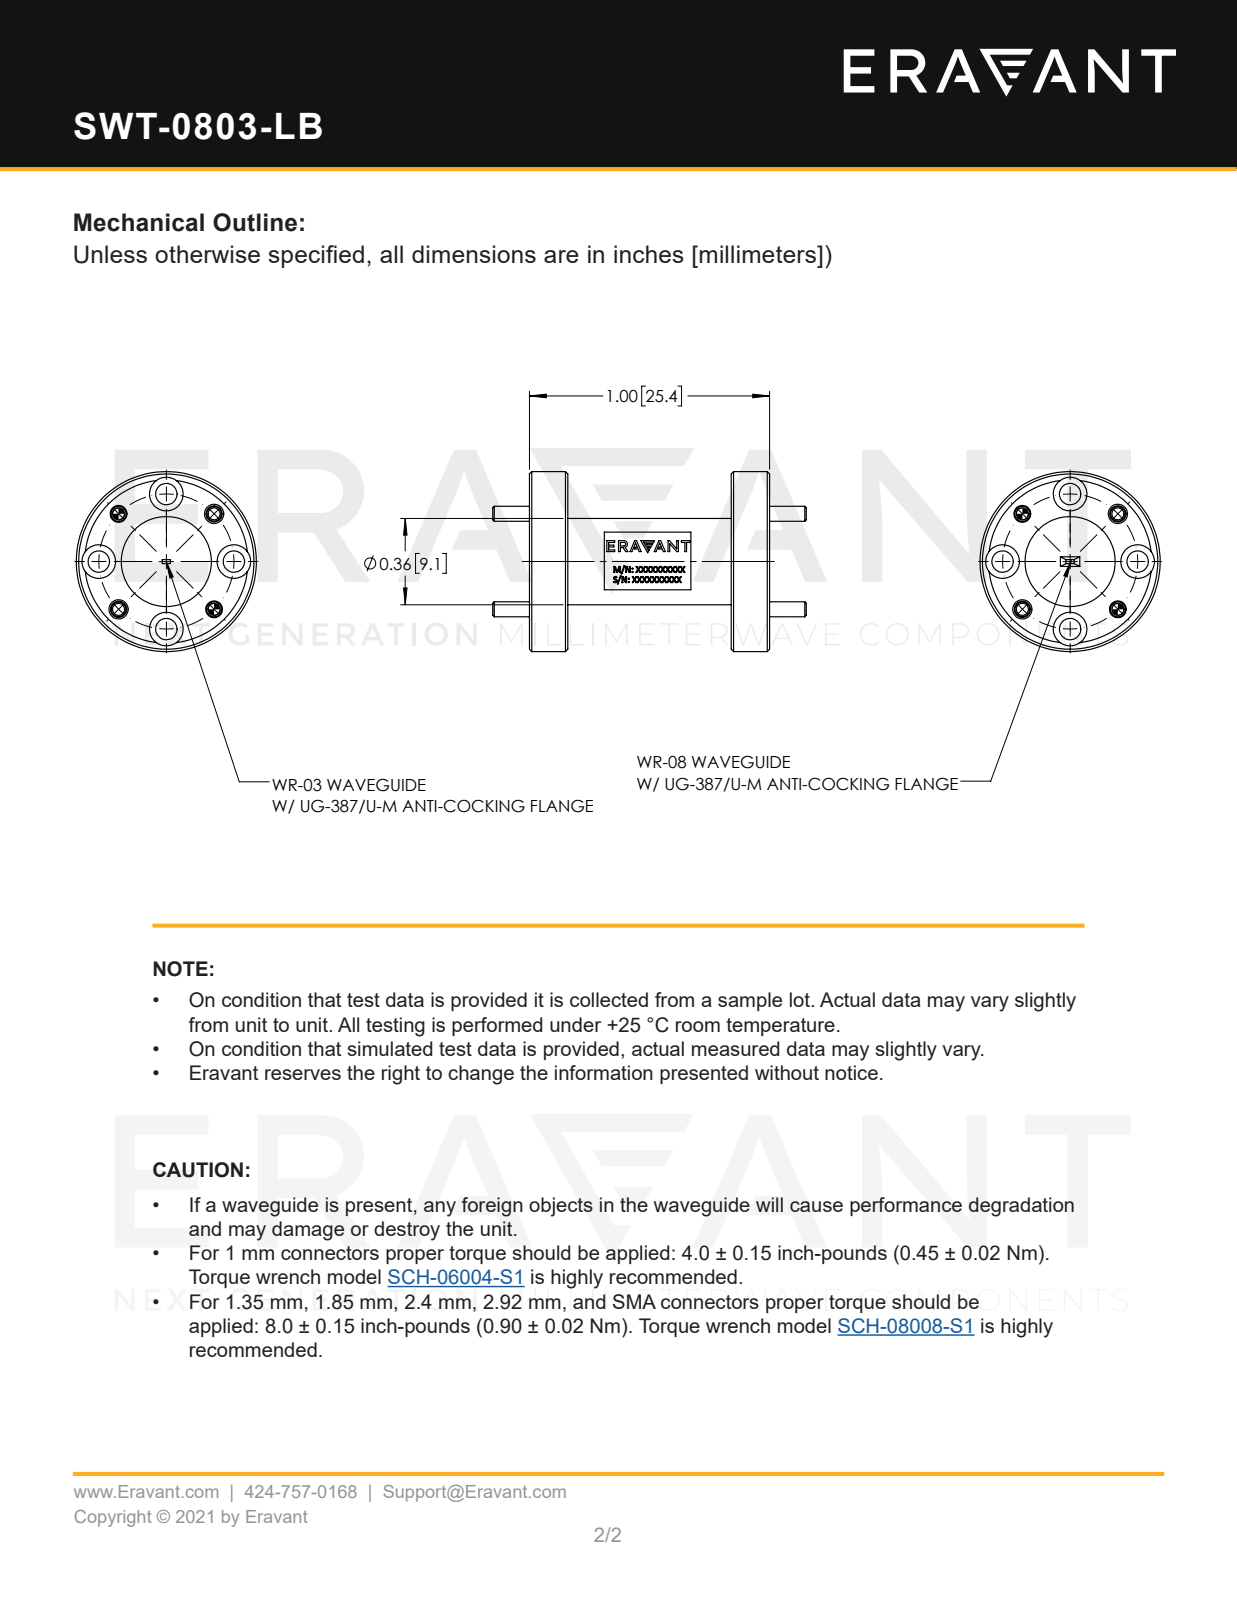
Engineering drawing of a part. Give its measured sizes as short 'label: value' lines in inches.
name: SWT-0803-LB
written by: SolidWorks 2021 (CONFIG_CONTROL_DESIGN)
unit: in
bodies: 5 solids, 148 faces (34 planar, 74 cylindrical, 40 other)
size: 1.305 × 0.75 × 0.75
volume: 0.19 in³; area: 3.866 in²
holes: 4× ⌀0.061, 4× ⌀0.067, 4× ⌀0.089, 4× ⌀0.14, 1× ⌀0.68
bosses: 4× ⌀0.063, 1× ⌀0.75, 1× ⌀0.375, 1× ⌀0.36
face distances: 0.14, 0.82, 0.02, 0.16, 0.84, 0.98, 0.68, 0.96, 1, 0.06
hole spacings: 0.215, 0.281, 0.398, 0.519, 0.562
